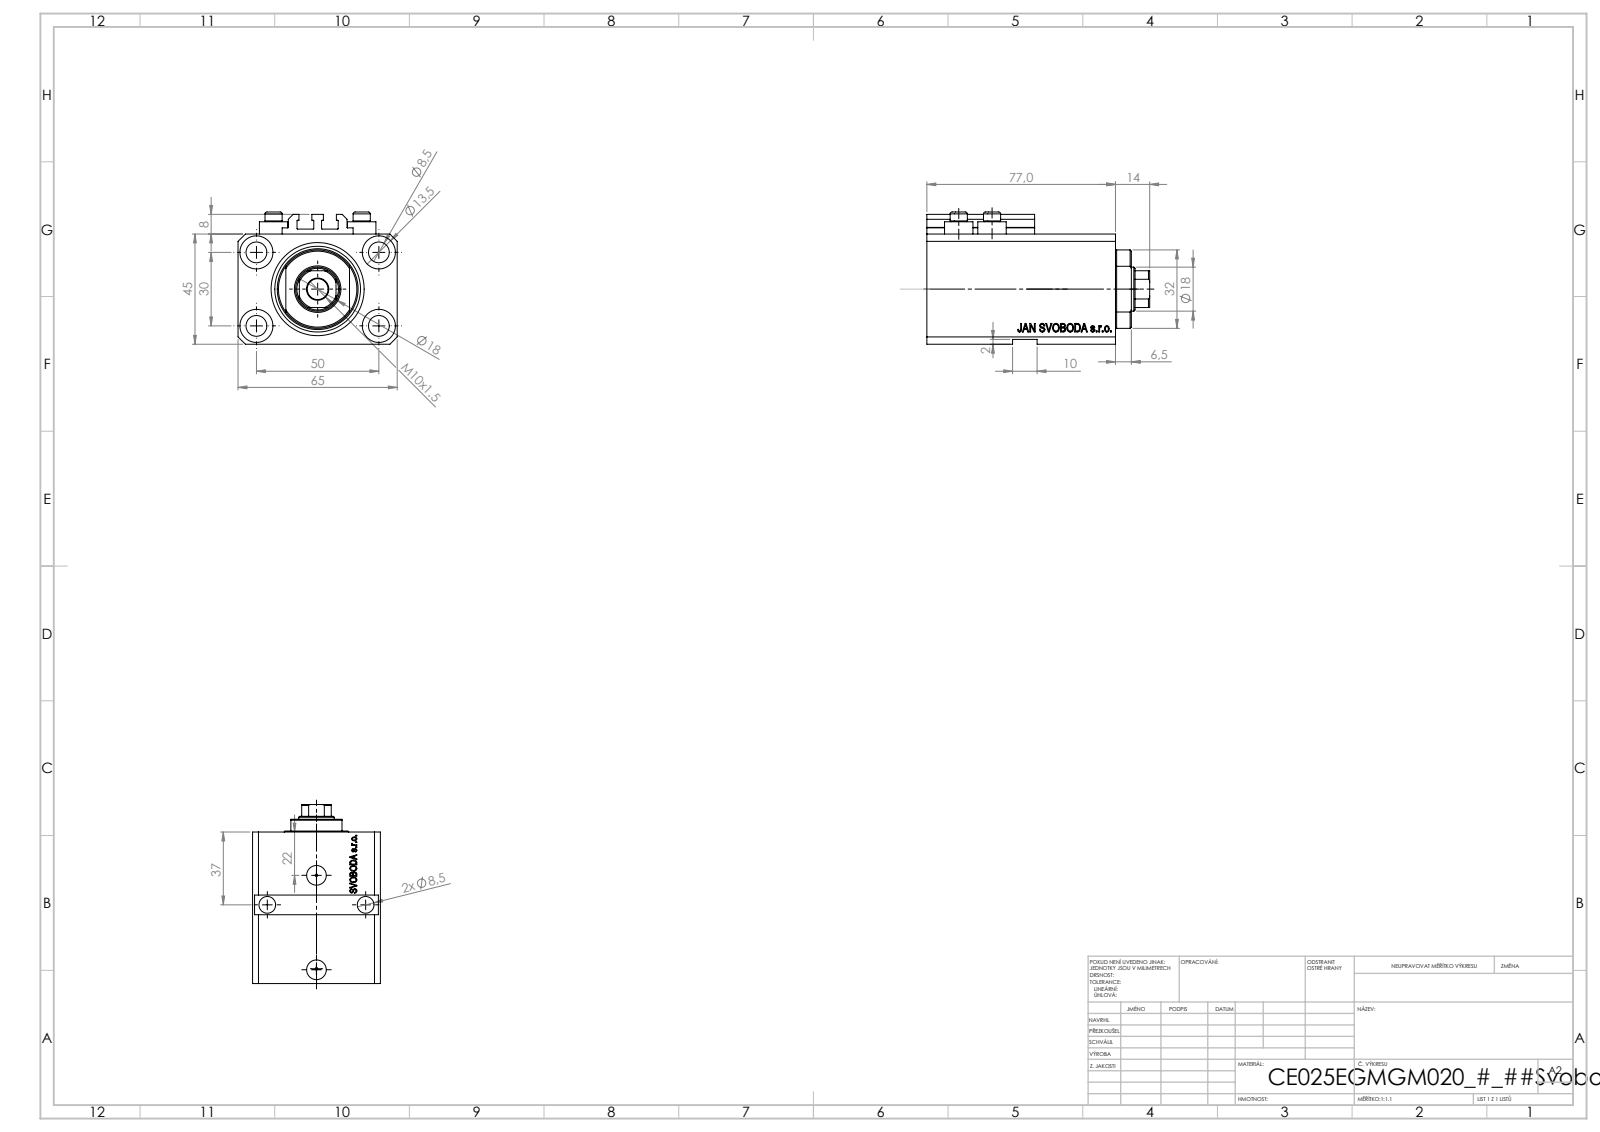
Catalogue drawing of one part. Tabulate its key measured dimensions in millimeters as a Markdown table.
| quantity | value |
| --- | --- |
| part name | V250CE_C_VCP; ALLEN BOLT V250CE; V250CE_VC_E; V250CE_E_Body |
| STEP written by | SolidWorks 2019 (CONFIG_CONTROL_DESIGN) |
| units | millimeters |
| bodies | 8 solids, 1067 faces (511 planar, 126 cylindrical, 430 other) |
| overall size | 91 × 65 × 54 |
| volume | 199 775 mm³ |
| surface area | 59 185 mm² |
| round holes (diameter × count) | 8.5 × 7, 1.25 × 4, 4 × 4, 13.5 × 4, 10 × 2, 13.16 × 2, 20 × 2, 18 × 1, 25 × 1, 38 × 1 |
| round bosses / shafts (diameter × count) | 11.6 × 4, 7 × 4 |
| partial cylindrical surfaces (radius × count) | 0.2 × 10, 8.5 × 1, 16 × 1 |
| main face-to-face distances | 45, 65, 63, 14, 77, 2, 6.9, 56.1, 70.1, 47 |
| hole center spacings | 29.15, 50, 13.6, 15.12, 18.81, 18.97, 26.22, 26.61 |
